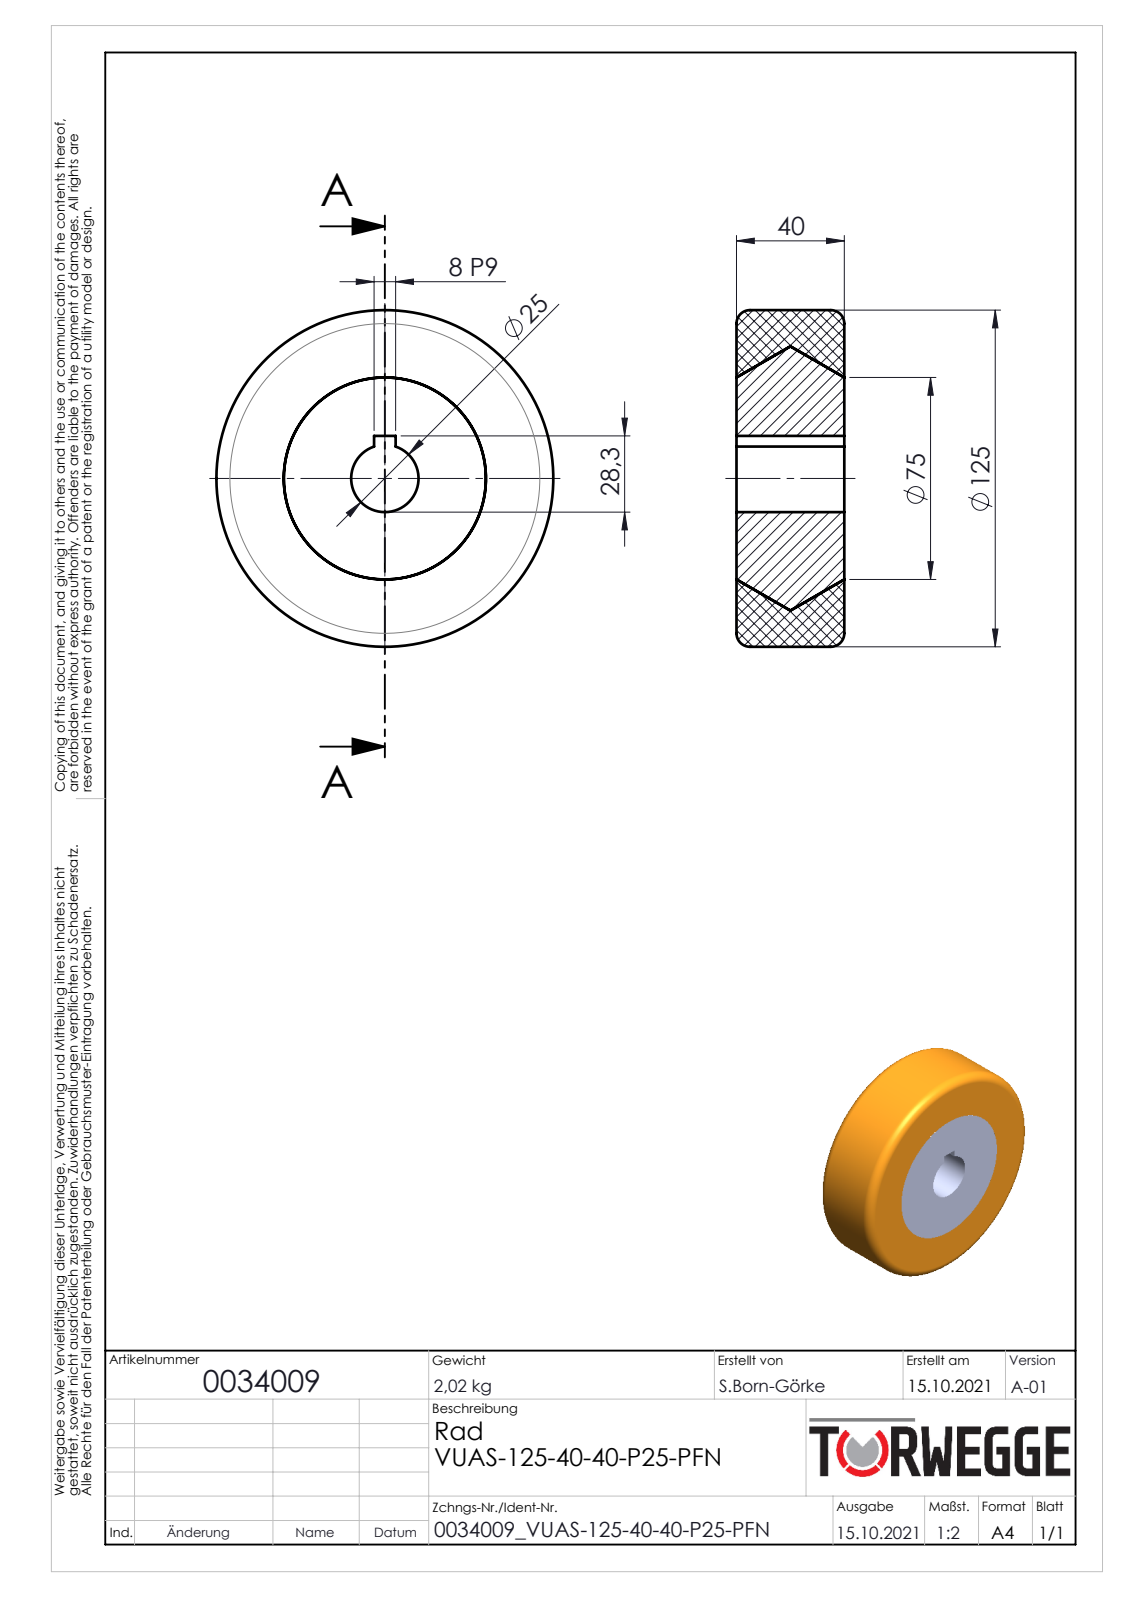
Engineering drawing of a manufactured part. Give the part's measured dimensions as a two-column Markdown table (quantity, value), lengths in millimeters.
| quantity | value |
| --- | --- |
| part name | 0034009 |
| STEP written by | SolidWorks 2020 (AUTOMOTIVE_DESIGN) |
| units | millimeters |
| bodies | 2 solids, 24 faces (7 planar, 5 cylindrical, 12 other) |
| overall size | 125 × 125 × 40 |
| volume | 465 975 mm³ |
| surface area | 66 075 mm² |
| round holes (diameter × count) | 25 × 1 |
| round bosses / shafts (diameter × count) | 125 × 1 |
| main face-to-face distances | 40, 8 |
